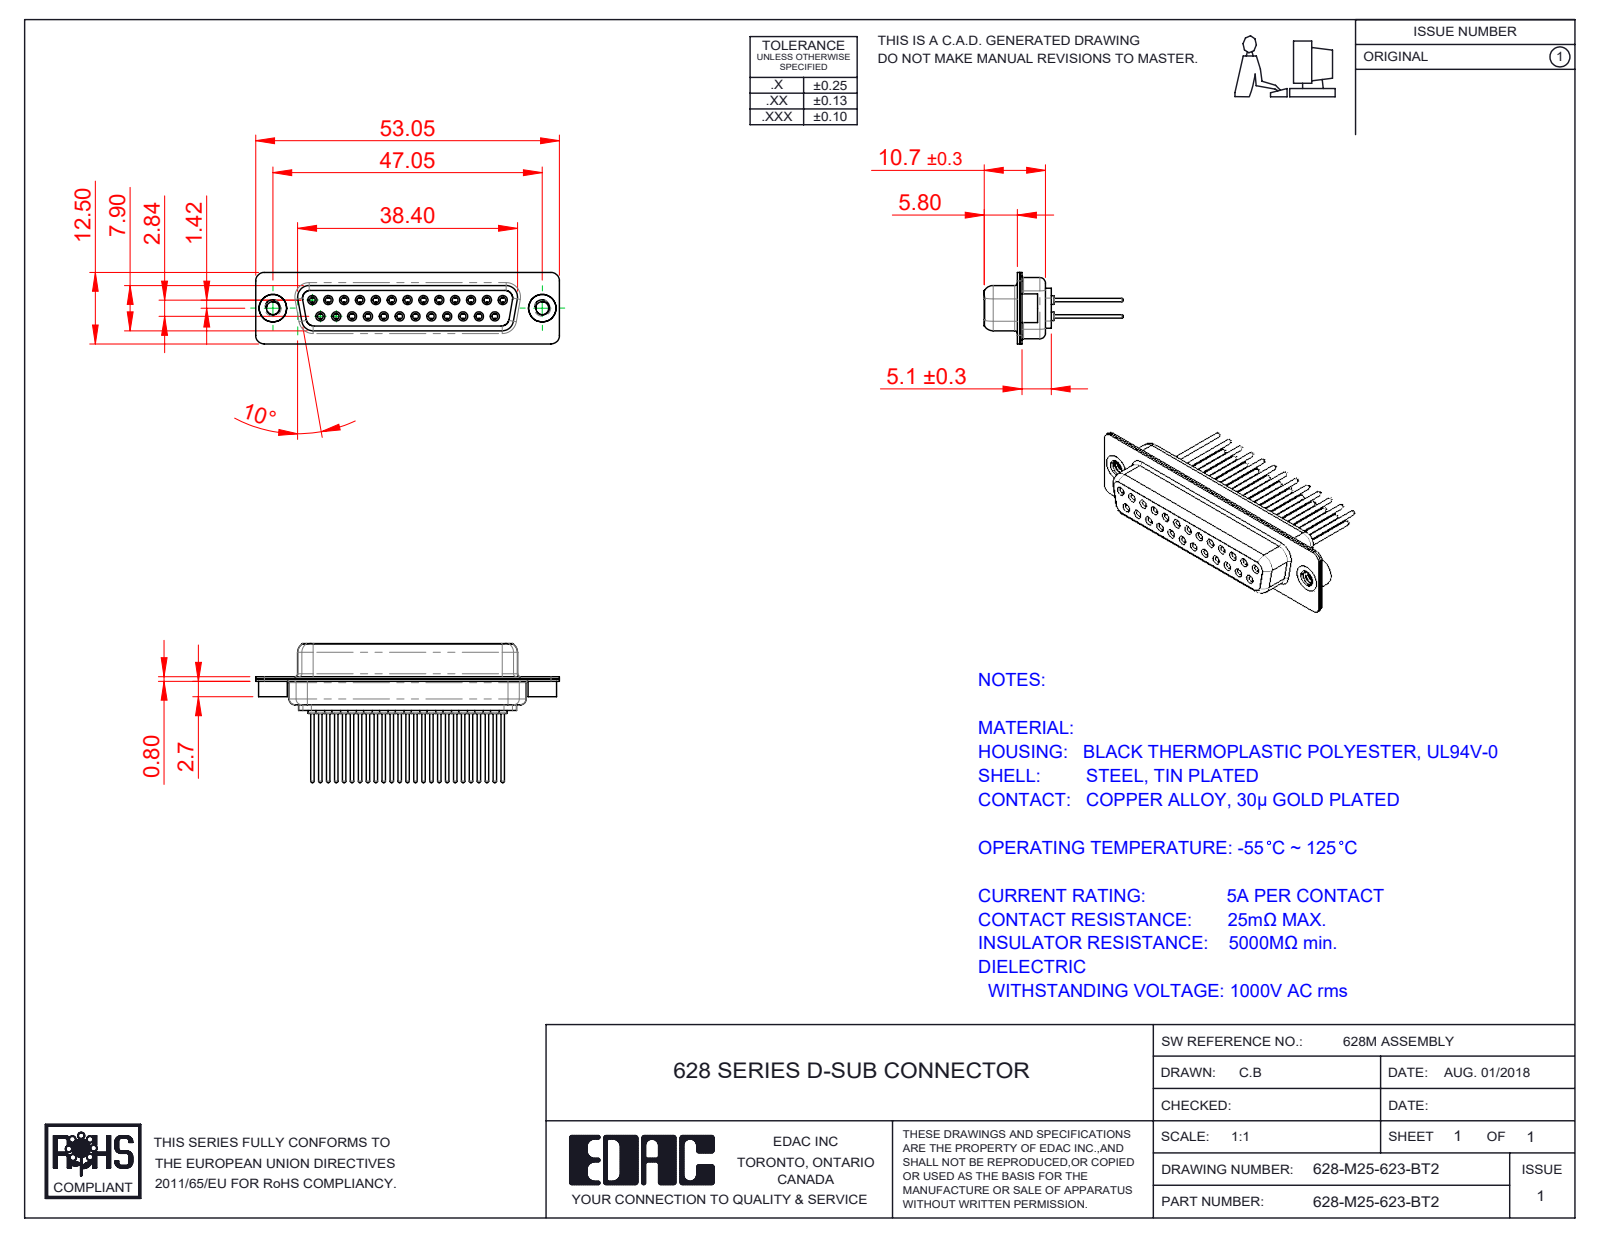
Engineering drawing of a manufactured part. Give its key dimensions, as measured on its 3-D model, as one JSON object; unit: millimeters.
{"part_name": "628M Contact Row 1_23; 628M 4-40 Threaded Rivet; 628M Shell Rear_25 Contacts; 628M Shell Front_25 Contacts (+3 more)", "step_written_by": "SolidWorks 2020 (CONFIG_CONTROL_DESIGN)", "units": "millimeters", "bodies": {"solids": 30, "faces": 1654, "planar": 442, "cylindrical": 612, "other": 600}, "overall_size": [53.05, 24.27, 12.5], "volume_mm3": 3788, "surface_area_mm2": 9465, "round_holes": [[1, 25], [1.1, 25], [1.7, 25], [1.8, 25], [2, 25], [2.26, 2], [4, 2], [4.8, 2]], "round_bosses_or_shafts": [[2.2, 25], [1.6, 25], [1.5, 25], [0.6, 25], [5, 2], [4.9, 2]], "partial_cylinders_radius": [[1.5, 16], [2, 12], [1.35, 8], [1.6, 8], [0.25, 4], [0.5, 4], [0.6, 4], [0.65, 4]], "face_to_face_distances": [0.4, 1.4, 0.45, 8.45, 8.9, 6.2, 1.8, 7.05, 1, 1.85], "hole_center_spacings": [3.16, 2.77, 5.54, 8.31, 11.08, 13.85, 5.04, 7.49]}
